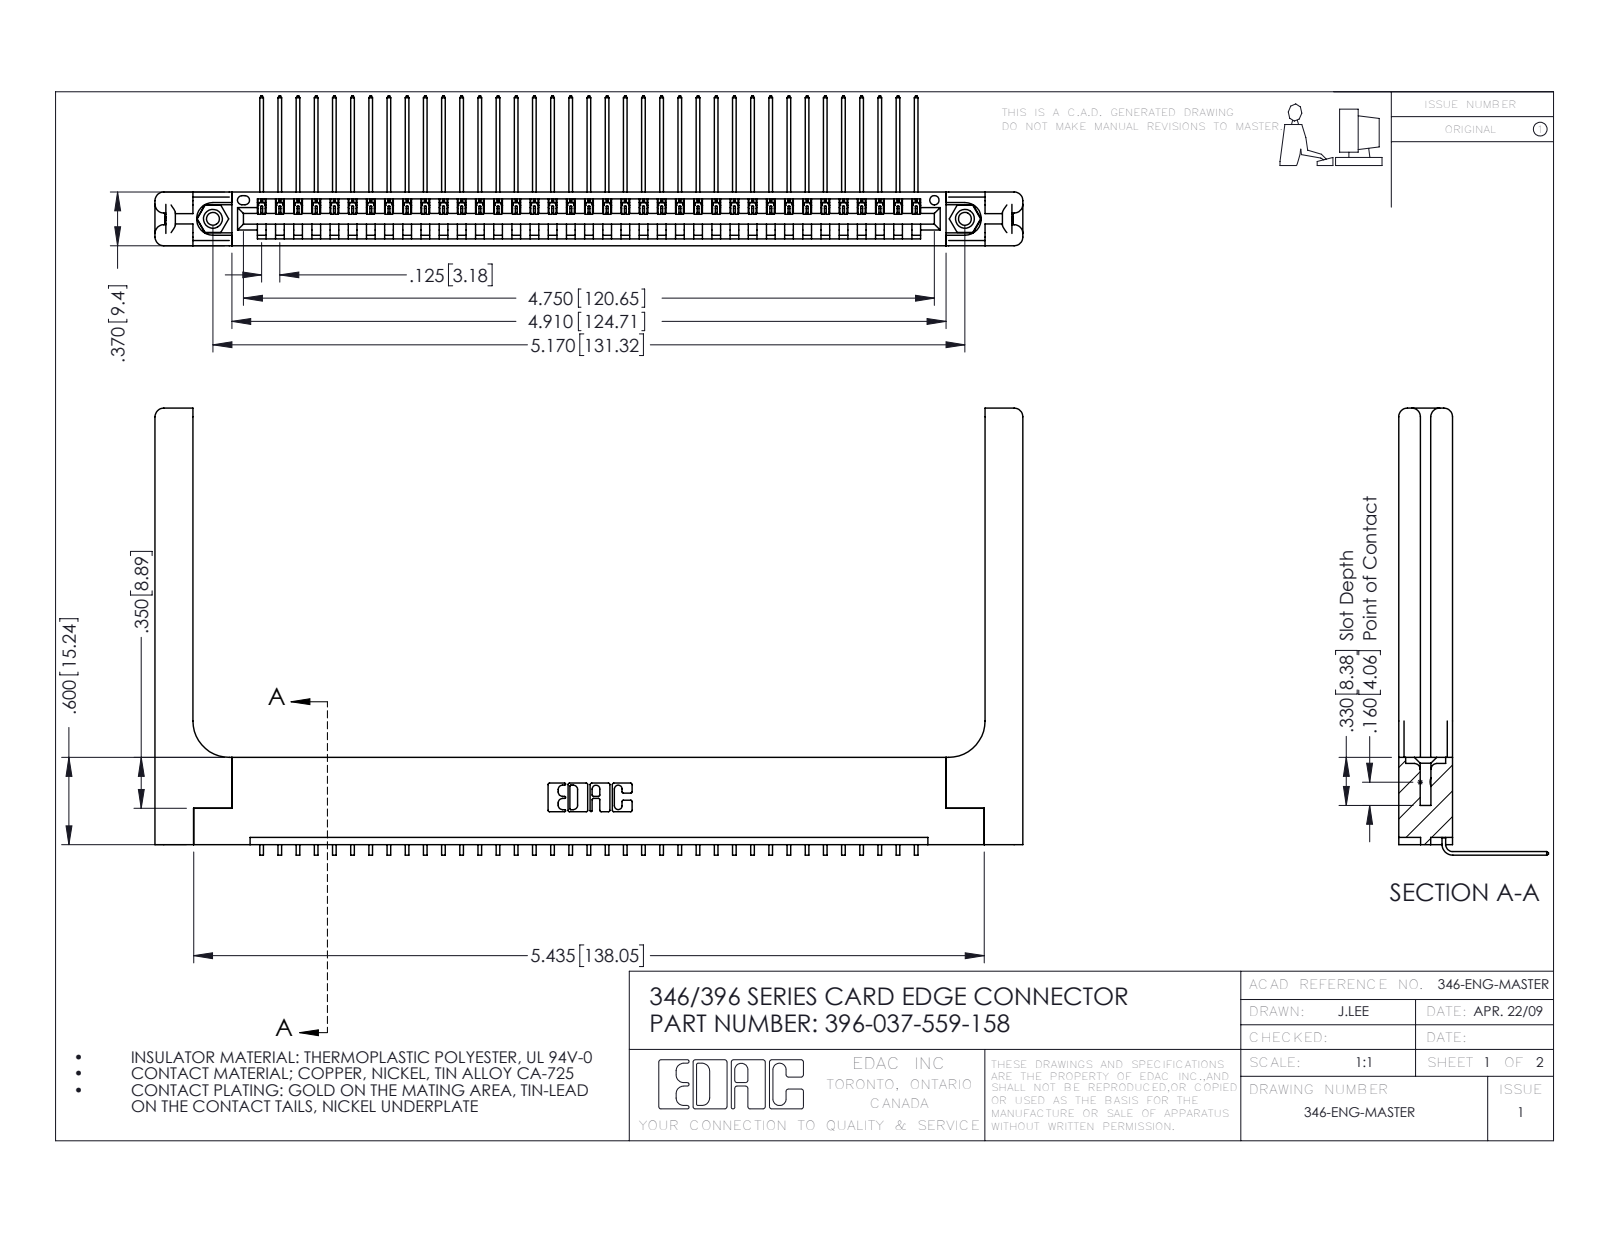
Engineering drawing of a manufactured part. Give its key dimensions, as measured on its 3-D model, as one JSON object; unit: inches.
{"part_name": "345-292-001_558 559 Tail - 1; 346 Part_Flush Mounting Lugs - 0.156 Dia-TH; 396-037-559-158; 345-250-001_345-250-001-102 (+1 more)", "step_written_by": "SolidWorks 2016 (CONFIG_CONTROL_DESIGN)", "units": "inches", "bodies": {"solids": 42, "faces": 2598, "planar": 1778, "cylindrical": 760, "other": 60}, "overall_size": [5.966, 3.073, 1.03], "volume_in3": 1.349, "surface_area_in2": 37.34, "round_holes": [[0.089, 2], [0.125, 2], [0.156, 2], [0.064, 1]], "round_bosses_or_shafts": [[0.155, 2]], "partial_cylinders_radius": [[0.006, 74], [0.01, 22], [0.06, 16], [0.007, 6], [0.031, 6], [0.026, 3], [0.03, 2], [0.031, 2]], "face_to_face_distances": [0.37, 0.048, 0.072, 0.322, 0.148, 0.15, 0.025, 0.25, 0.298, 0.222], "hole_center_spacings": [0.246, 4.961, 5.17]}
